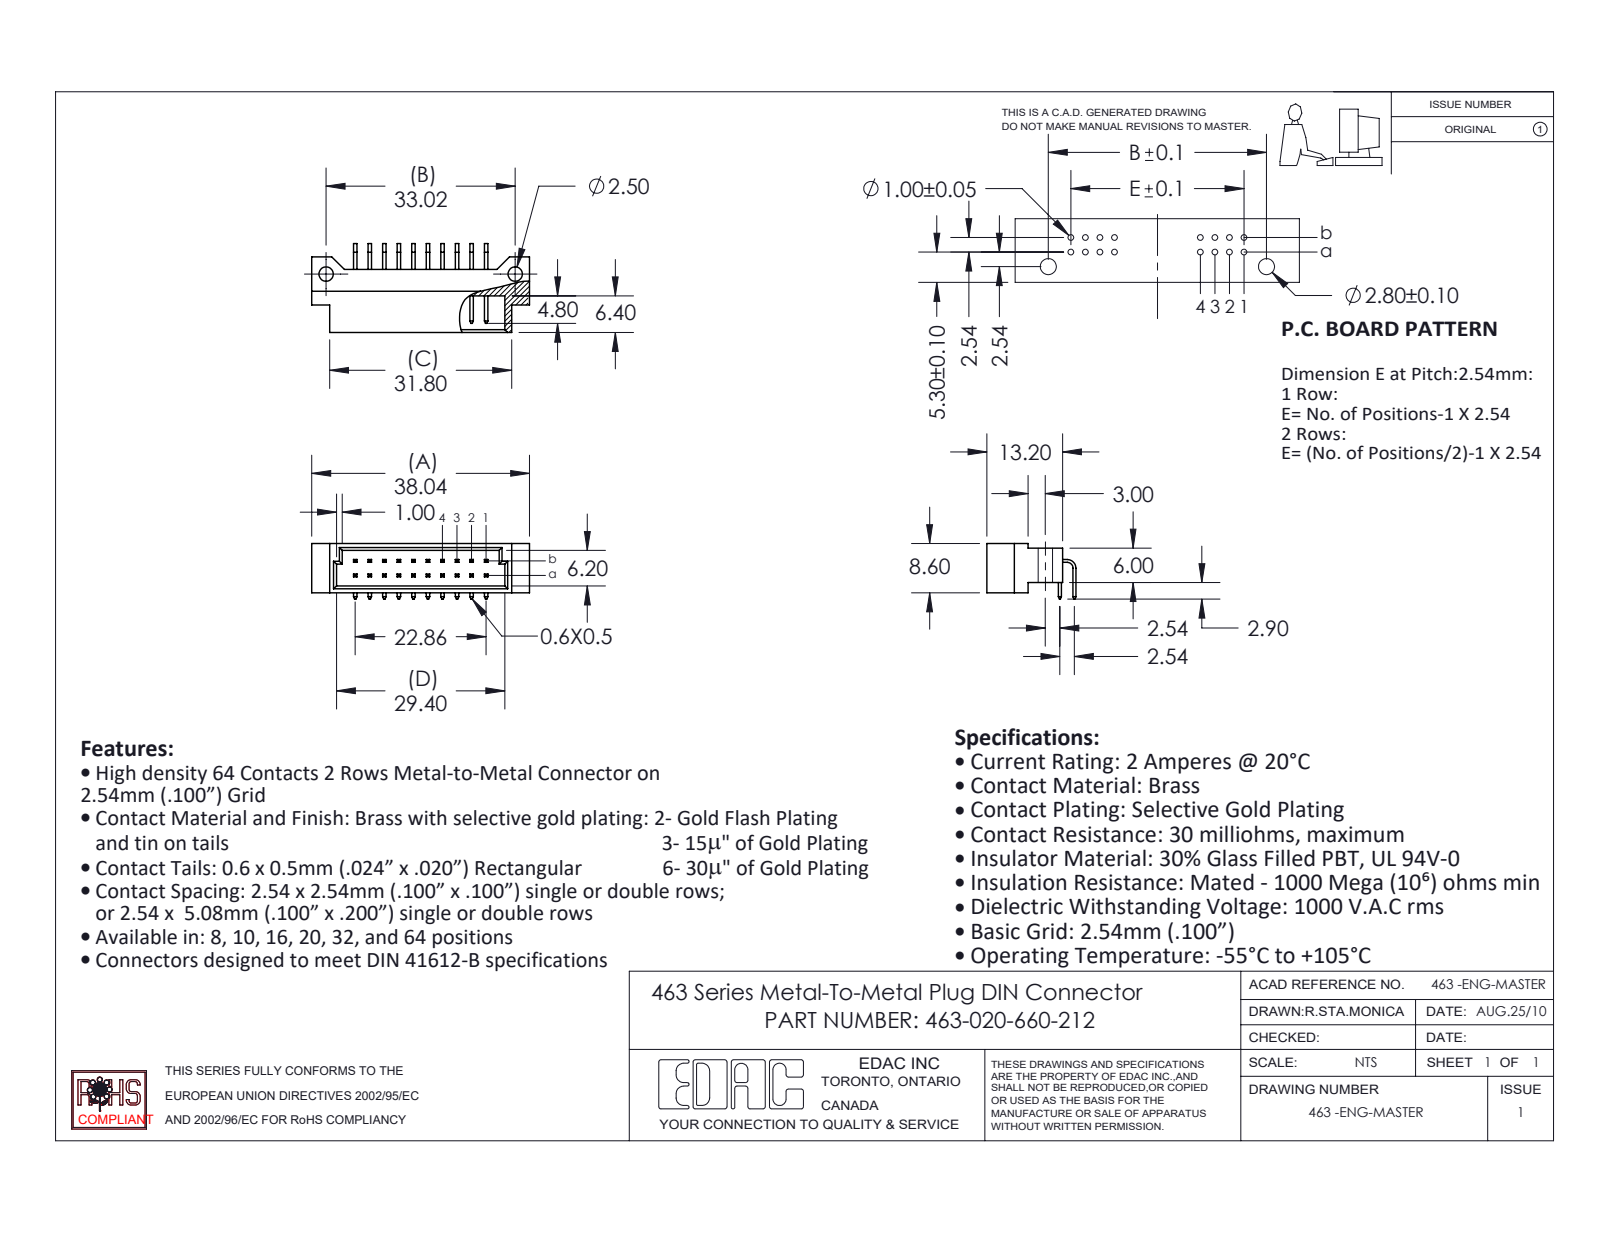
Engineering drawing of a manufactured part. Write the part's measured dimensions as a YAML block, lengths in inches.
part_name: "463-290-2; 463 Part_20; 463-290-1; 463-020-660-212"
step_written_by: "SolidWorks 2020 (CONFIG_CONTROL_DESIGN)"
units: inches
bodies: {solids: 21, faces: 479, planar: 435, cylindrical: 44, other: 0}
overall_size: [1.498, 0.611, 0.382]
volume: 0.119
surface_area: 4.852
round_holes:
  - {diameter: 0.098, count: 2}
partial_cylinders:
  - {radius: 0.04, count: 2}
  - {radius: 0.06, count: 2}
face_to_face_distances: [0.1, 0.047, 0.291, 0.031, 0.339, 0.024, 0.02, 0.244, 0.2, 0.236]
hole_center_spacings: [1.3]
